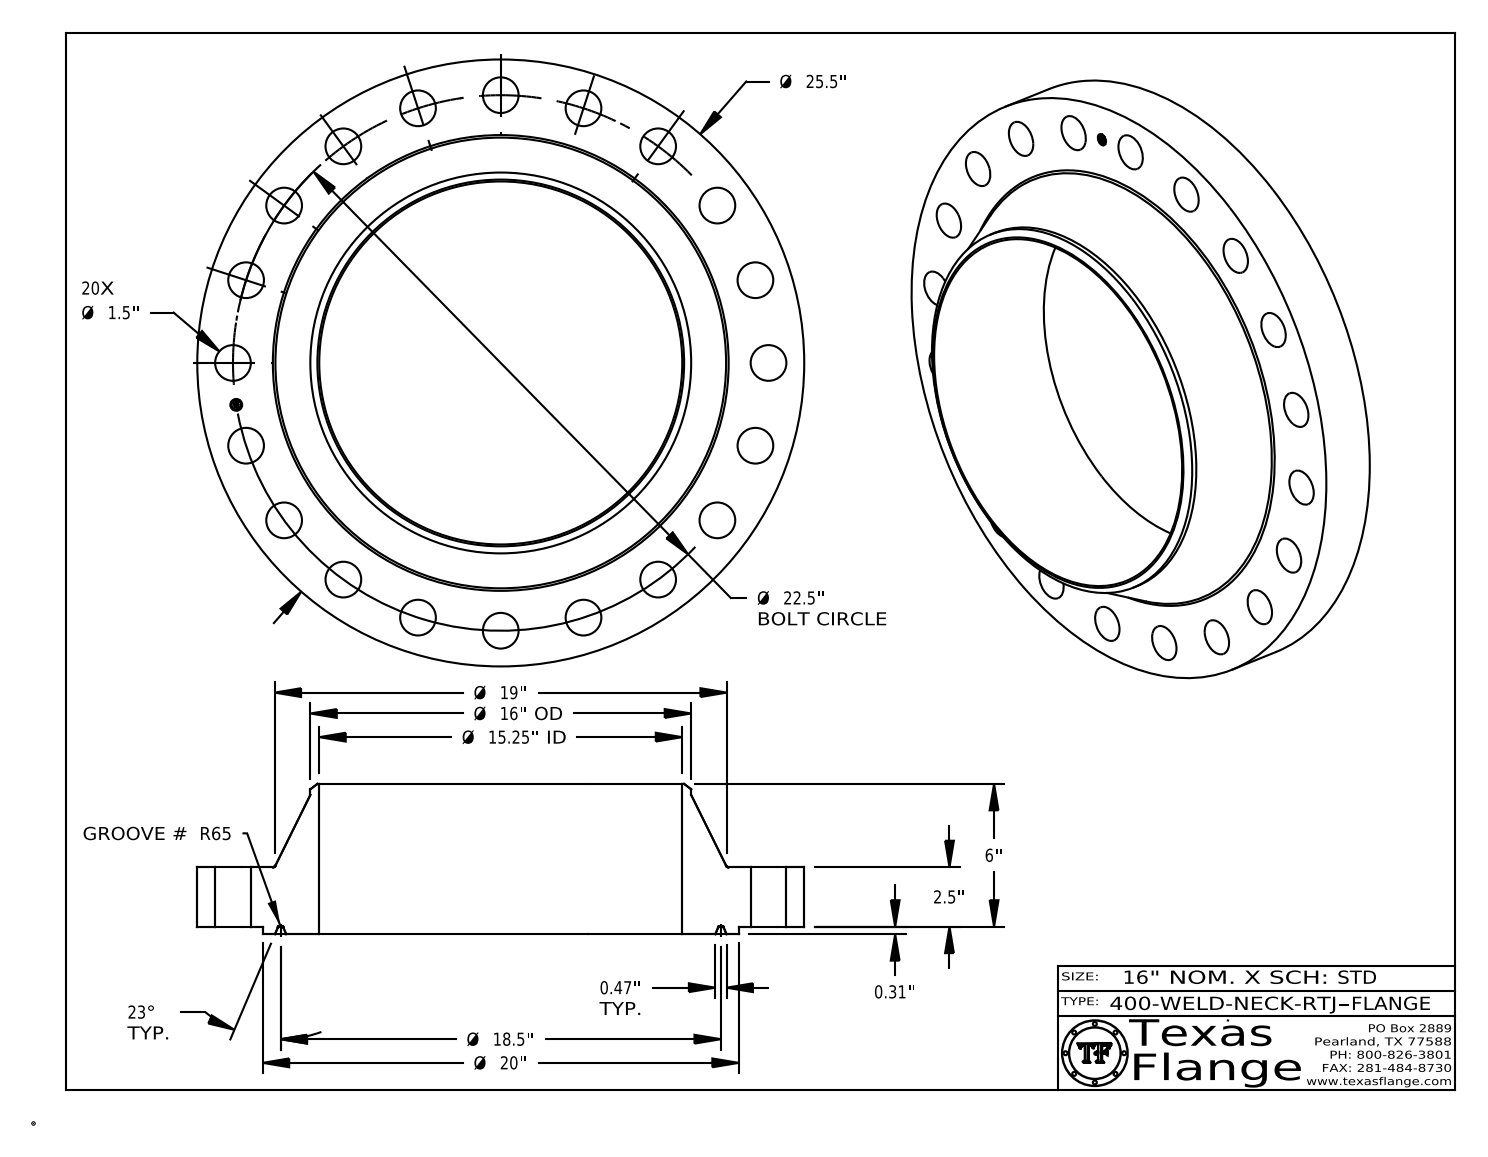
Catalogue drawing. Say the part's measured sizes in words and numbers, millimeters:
The part is named "400-WELD-NECK-RTJ". Its 3-D file was written by "CATIA V5 STEP AP214 (AUTOMOTIVE_DESIGN)". It is 1 solid with 453 faces: 371 planar, 68 cylindrical and 14 other. Overall it measures 647.7 by 647.7 by 160.4 millimeters. Its volume is 15 590 000 cubic millimeters and its surface area 958 700 square millimeters. Round holes: 20 of diameter 38.1, 1 of diameter 12.6, 1 of diameter 387.4. Round bosses or shafts: 8 of diameter 0.8, 1 of diameter 647.7, 1 of diameter 508, 1 of diameter 406.4, 1 of diameter 9.9. The main face-to-face distances are 63.5, 8, 71.5, 160.4, 152.4, 88.9, 71.1, 63.1, 0.4, 89.3. The hole center spacings are 285.8, 176.6, 335.9, 89.4, 462.4, 509.2, 543.5, 564.5.
